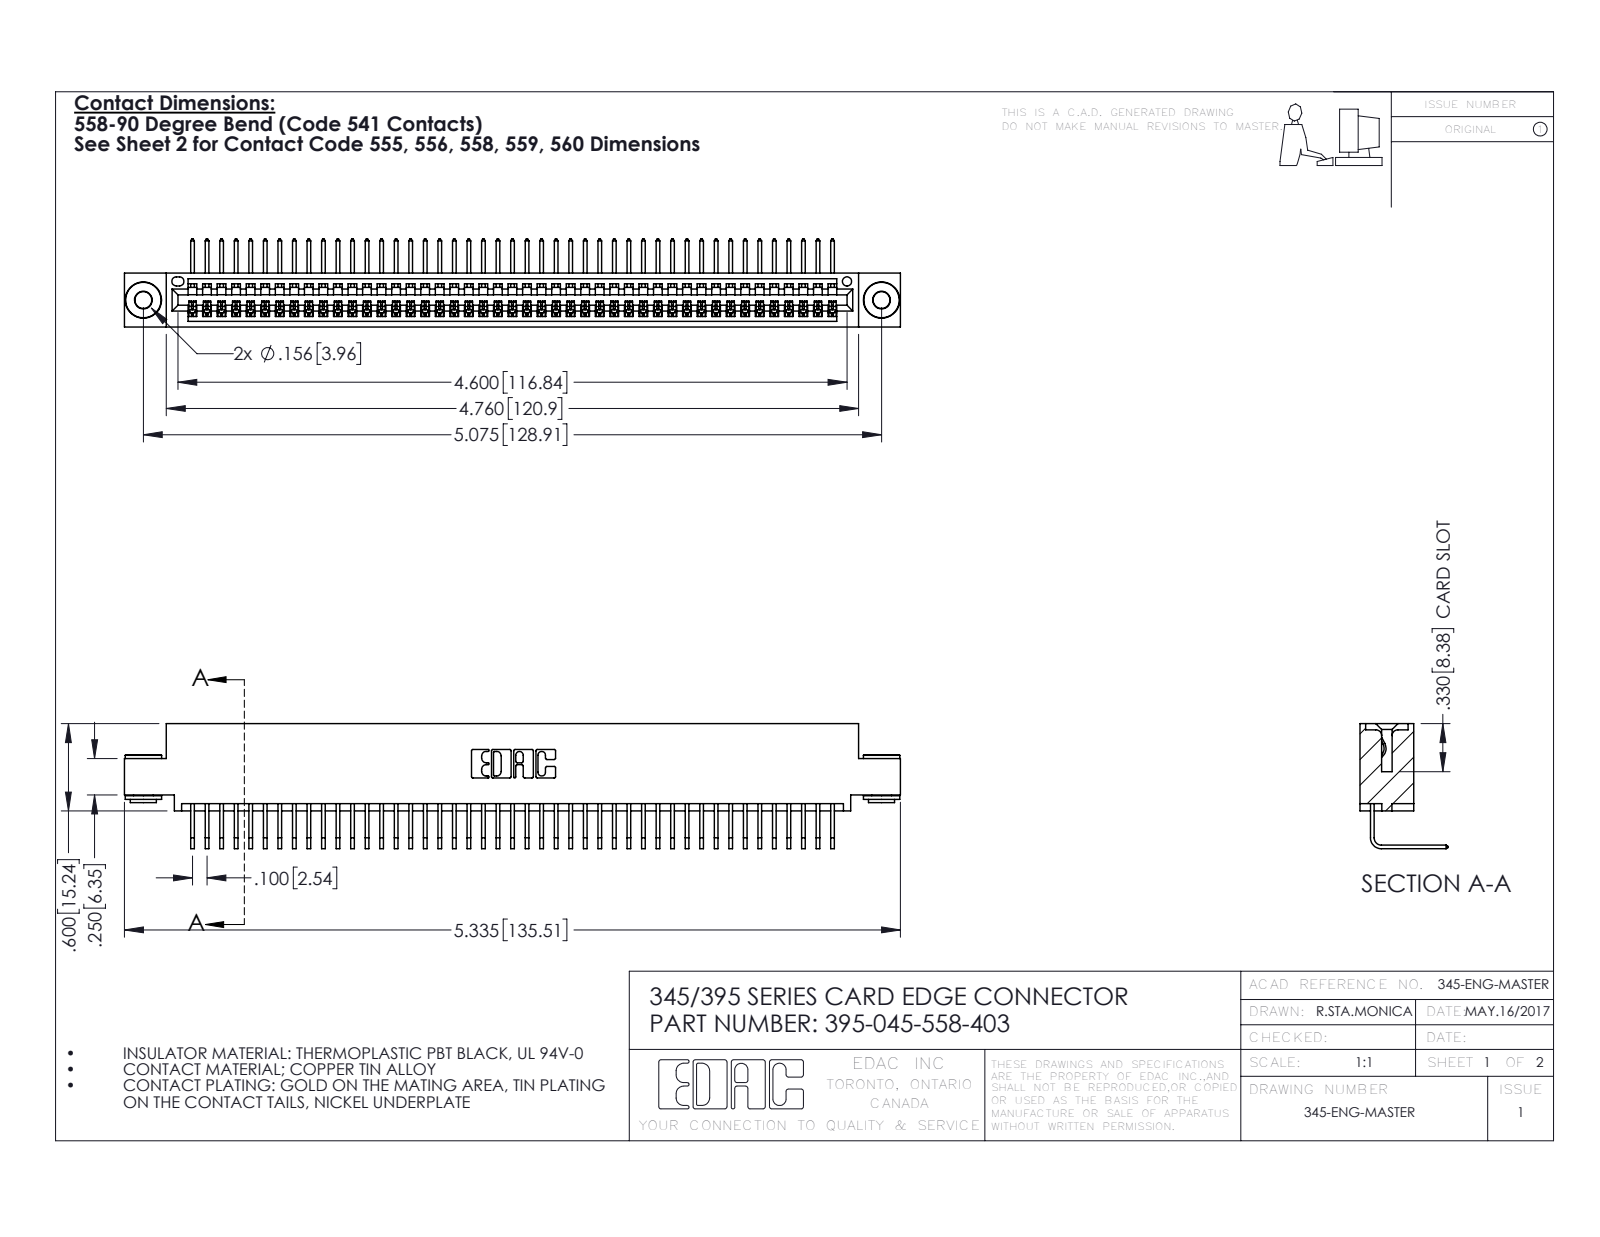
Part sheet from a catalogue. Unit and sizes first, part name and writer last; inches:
Units: inches
Overall size (bounding box): 5.335 × 0.859 × 0.605
Round holes (diameter × count): ⌀0.116 ×2, ⌀0.156 ×2, ⌀0.064 ×1
Round bosses / shafts (diameter × count): ⌀0.25 ×2, ⌀0.18 ×2, ⌀0.136 ×2
Partial cylindrical surfaces — rounded edges, fillets, slot ends (radius × count): R0.006 ×90, R0.01 ×22, R0.007 ×6, R0.031 ×6, R0.026 ×3, R0.031 ×2, R0.04 ×2, R0.014 ×1
Main face-to-face distances: 0.072, 0.298, 0.37, 0.2, 0.025, 0.098, 0.272, 0.225, 0.149, 0.072
Hole centre spacings: 0.27, 4.839, 5.075
Volume: 0.793 in³ · Surface area: 28.65 in²
Bodies: 48 solids, 2868 faces (1984 planar, 876 cylindrical, 8 other)
Part name (STEP PRODUCT): 345-250-002_345-250-002-102; 345-292-001_558 Tail - 2; 395-045-558-403; 345 Part_0.110 Offset - 0.156 Dia-TH
STEP written by: SolidWorks 2016 (CONFIG_CONTROL_DESIGN)
